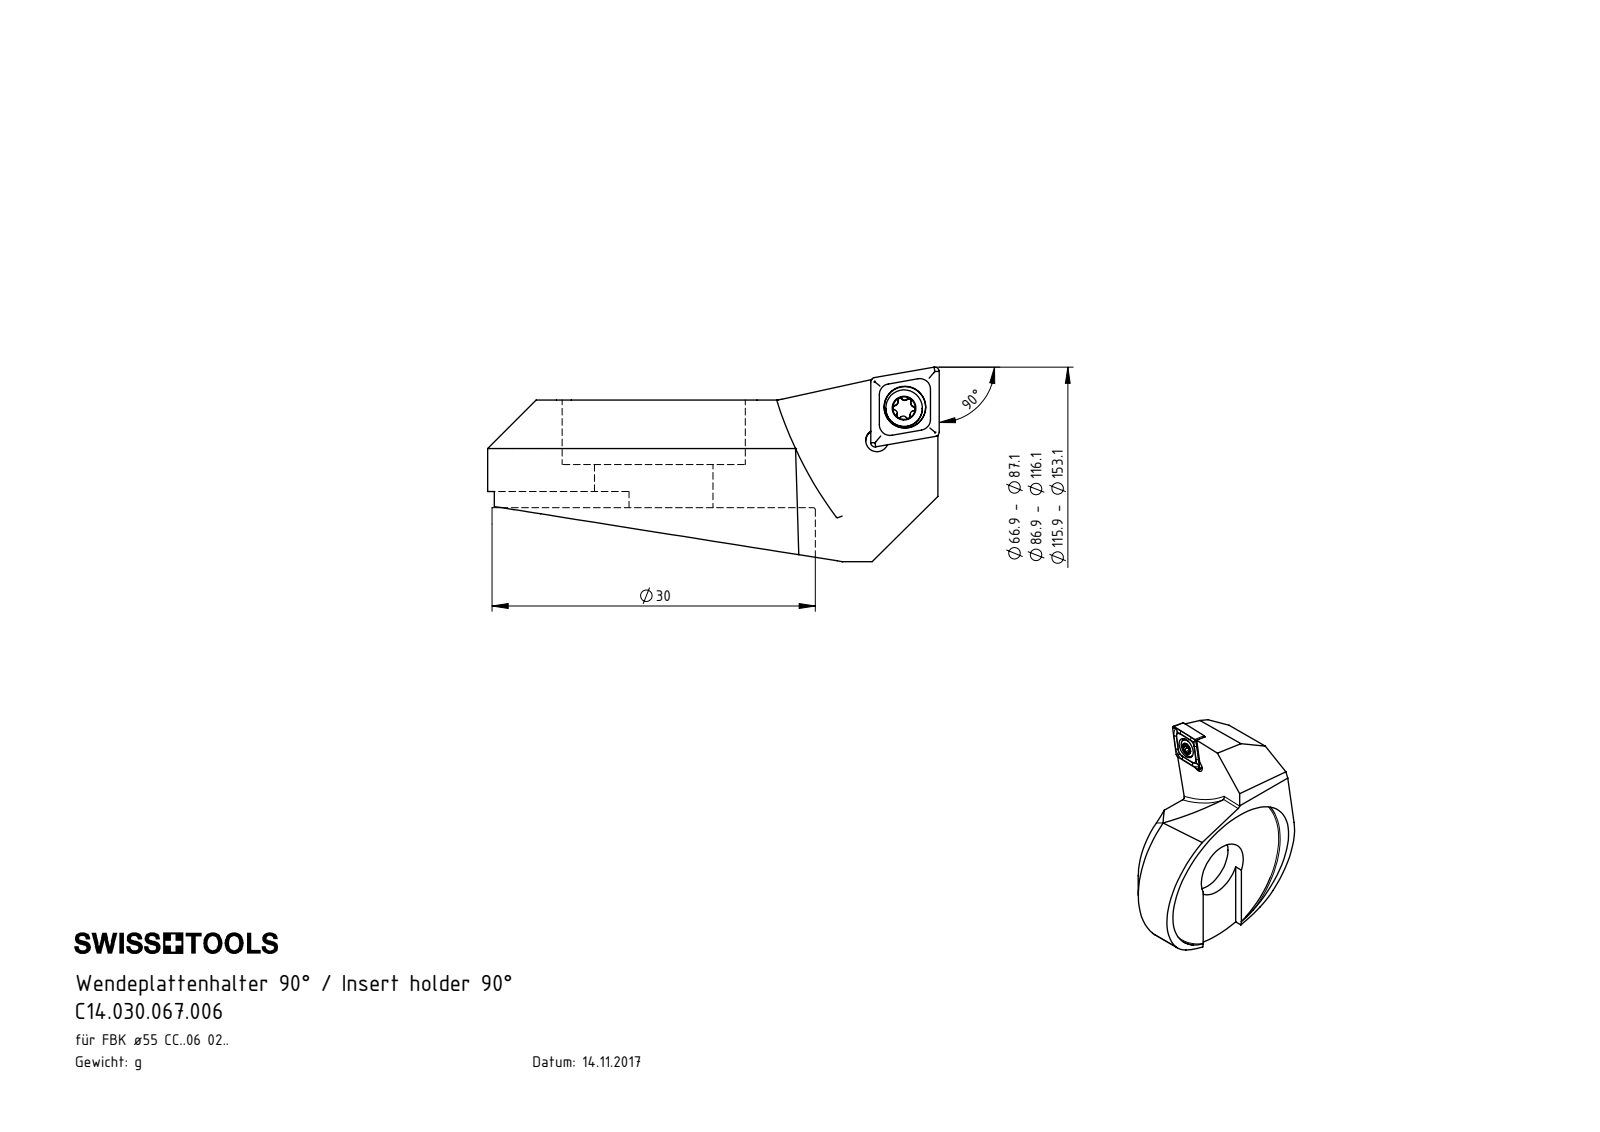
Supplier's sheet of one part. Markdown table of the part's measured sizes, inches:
| quantity | value |
| --- | --- |
| part name | F55-WCA.001.013_D_fertigbearbeitet; CCMT060204; WCA-ER2.001.005_A; C14.030.067.006 |
| STEP written by | SolidWorks 2017 (CONFIG_CONTROL_DESIGN) |
| units | inches |
| bodies | 5 solids, 153 faces (48 planar, 48 cylindrical, 57 other) |
| overall size | 1.65 × 1.303 × 0.711 |
| volume | 0.49 in³ |
| surface area | 7.082 in² |
| round holes (diameter × count) | 0.081 × 1, 0.083 × 1, 0.11 × 1, 0.152 × 1, 0.433 × 1, 0.669 × 1, 1.181 × 1 |
| round bosses / shafts (diameter × count) | 0.134 × 1, 0.098 × 1 |
| partial cylindrical surfaces (radius × count) | 0.008 × 6, 0.014 × 5, 0.02 × 2, 0.394 × 2, 0.014 × 1, 0.041 × 1, 0.197 × 1, 0.652 × 1 |
| main face-to-face distances | 0.394, 0.354, 0.039, 0.197, 0.236, 0.157, 0.335, 0.295, 0.098, 0.059 |
| hole center spacings | 0.154, 0.159 |
